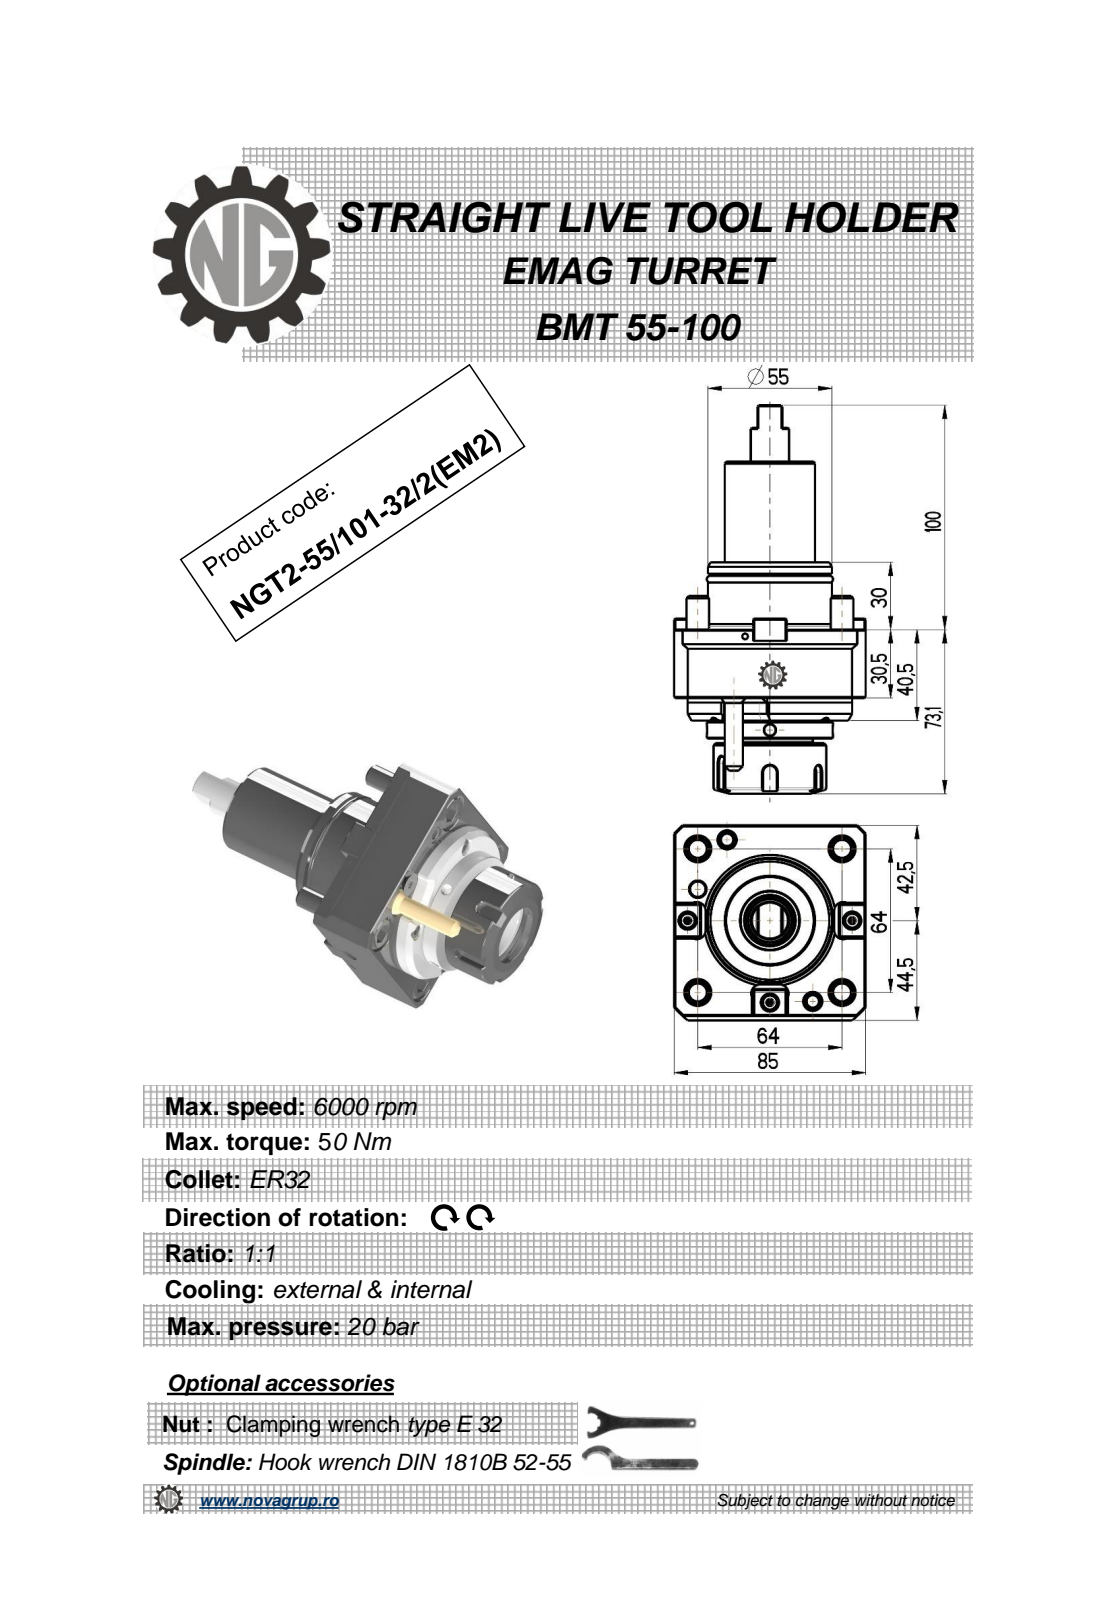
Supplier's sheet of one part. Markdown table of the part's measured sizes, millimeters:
| quantity | value |
| --- | --- |
| part name | NGT2_55_101_32_1_EM2 |
| STEP written by | PRO/ENGINEER BY PARAMETRIC TECHNOLOGY CORPORATION, 2010280 (CONFIG_CONTROL_DESIGN) |
| units | millimeters |
| bodies | 2 solids, 304 faces (140 planar, 67 cylindrical, 97 other) |
| overall size | 173.1 × 87 × 85 |
| volume | 464 375 mm³ |
| surface area | 54 560 mm² |
| round holes (diameter × count) | 5 × 3, 3 × 1, 6.8 × 1, 27 × 1 |
| round bosses / shafts (diameter × count) | 10 × 4, 73 × 1, 56 × 1, 55 × 1, 54.4 × 1, 50 × 1, 42 × 1, 40 × 1 |
| partial cylindrical surfaces (radius × count) | 0.22 × 6, 3 × 5, 0.8 × 2, 6 × 2, 57.5 × 1 |
| main face-to-face distances | 30.5, 85, 10, 40.5, 87, 18, 20.1, 8, 10.5, 48.5 |
| hole center spacings | 34.93, 37.12, 50.12 |
